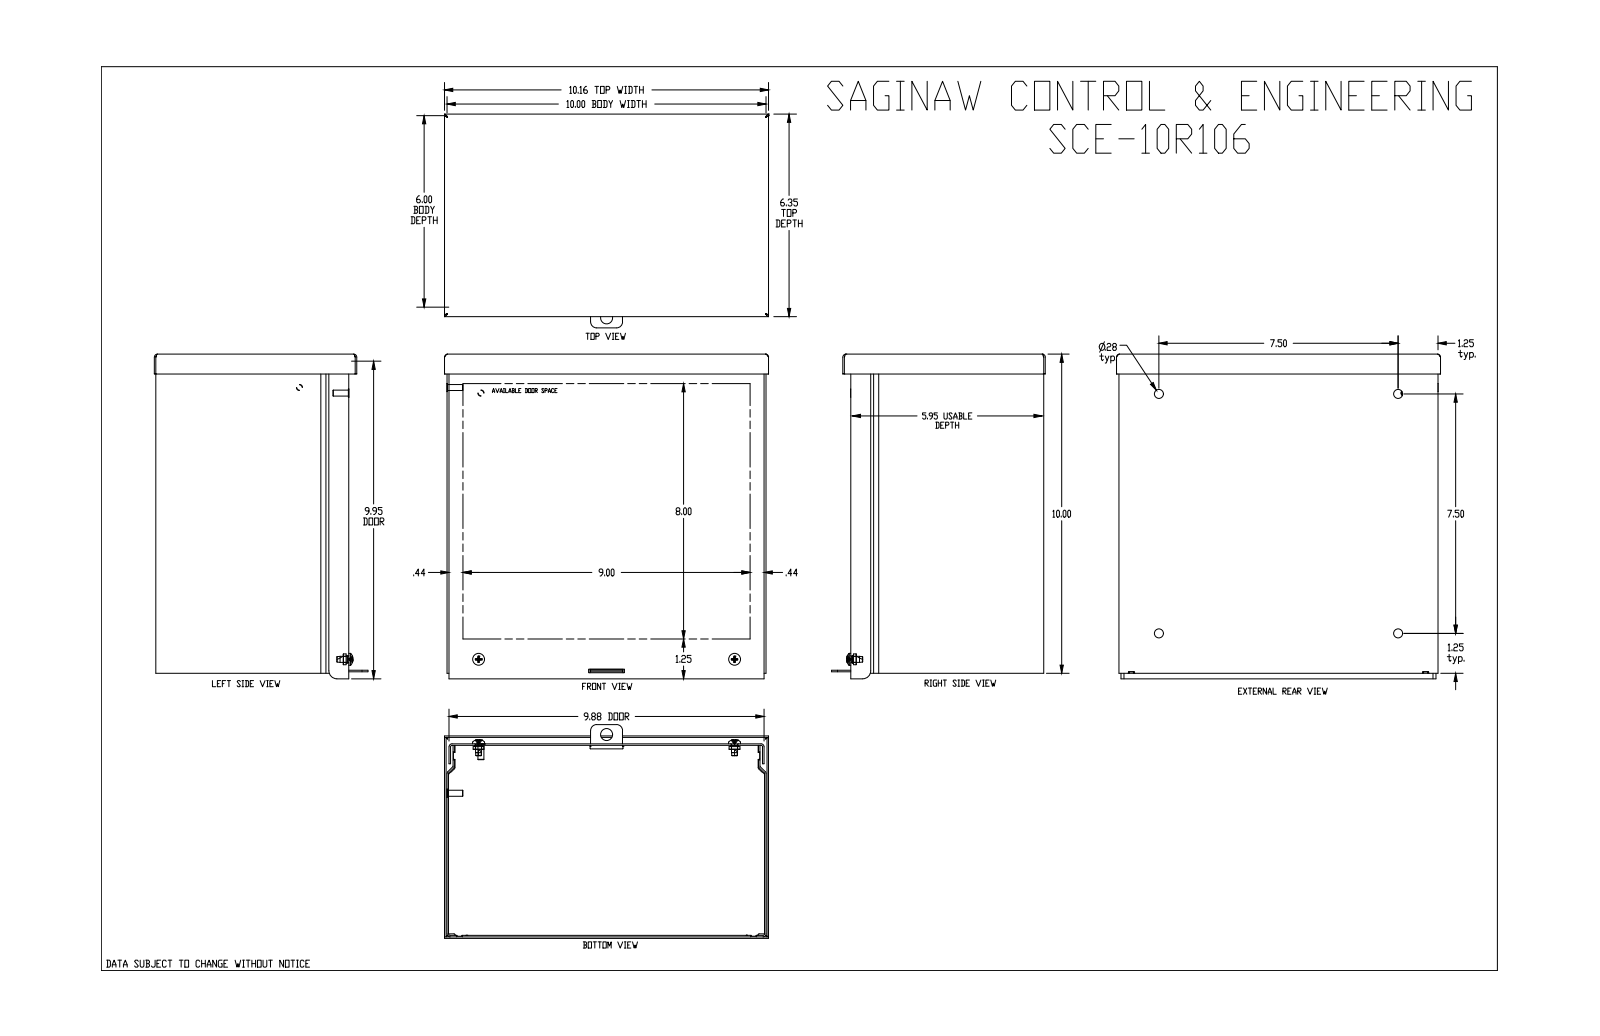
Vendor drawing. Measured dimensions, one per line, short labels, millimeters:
name: SCE-10R106
written by: SolidWorks 2019 (AUTOMOTIVE_DESIGN)
unit: mm
bodies: 11 solids, 398 faces (181 planar, 143 cylindrical, 74 other)
size: 258.4 × 258 × 170.1
volume: 405 100 mm³; area: 644 000 mm²
holes: 4× ⌀7.1, 3× ⌀4.8, 2× ⌀6.4, 1× ⌀4.8, 1× ⌀4.9, 1× ⌀9.5
bosses: 4× ⌀4.8, 2× ⌀9.5, 2× ⌀8.6, 2× ⌀6.5, 2× ⌀6.3
rounds: 32× R0.4, 12× R3.2, 8× R1.2, 8× R1.5, 8× R2.4, 4× R0.6, 4× R1.6, 4× R1.9
face distances: 1.2, 152.4, 252.8, 254, 153.6, 151.2, 1.5, 251.6, 251.3, 252.5
hole spacings: 190.5, 21.7, 198.2, 211.3, 269.4, 288.9, 4.8, 33.9
